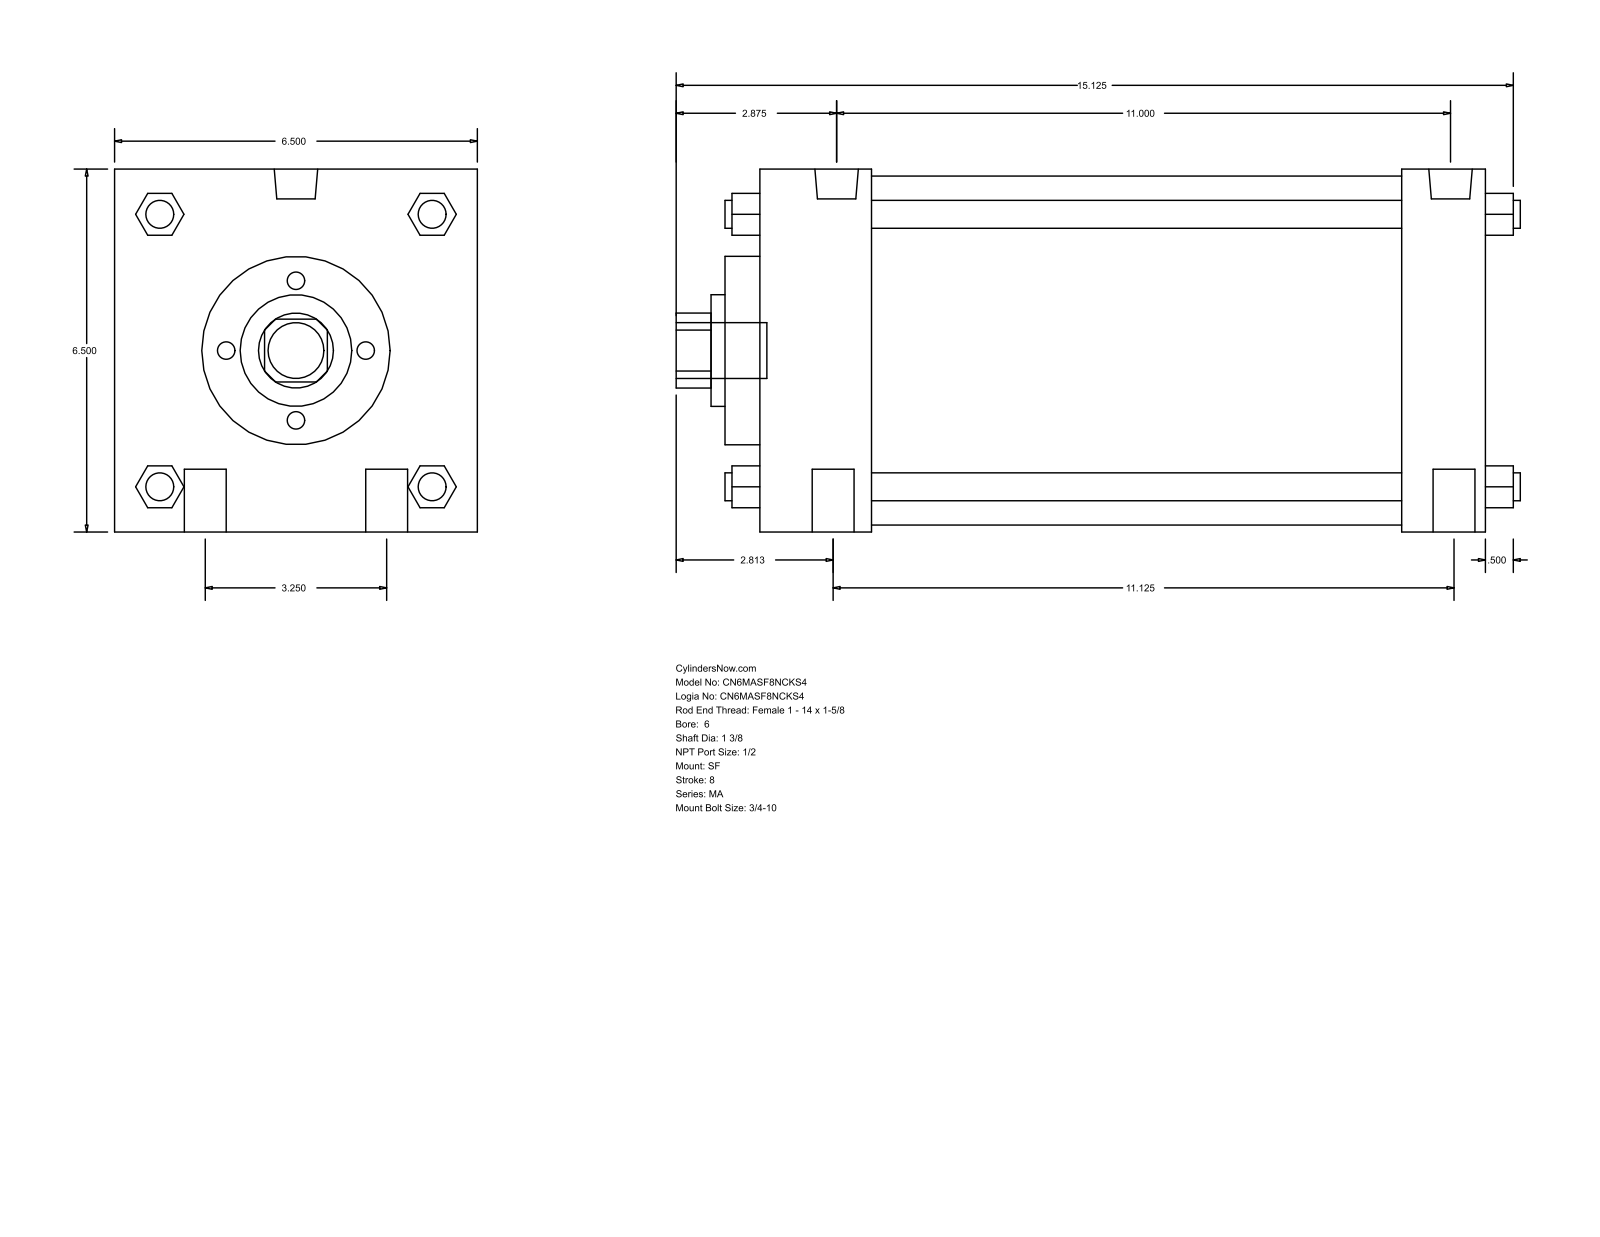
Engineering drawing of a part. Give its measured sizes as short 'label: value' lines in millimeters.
name: MA_SF__0600_1.375
written by: GSSL Pune (CONFIG_CONTROL_DESIGN)
unit: mm
bodies: 0 solids, 126 faces (95 planar, 31 cylindrical, 0 other)
size: 384.18 × 165.1 × 165.1
holes: 1× ⌀34.92, 1× ⌀50.8, 1× ⌀85.72, 1× ⌀158.75
bosses: 4× ⌀19.05, 4× ⌀12.7, 2× ⌀19.77, 2× ⌀17.46, 1× ⌀25.4
rounds: 1× R17.06
face distances: 165.1, 330.2, 292.1, 50.8, 38.1, 241.3, 279.4, 15.87, 66.67, 307.97
